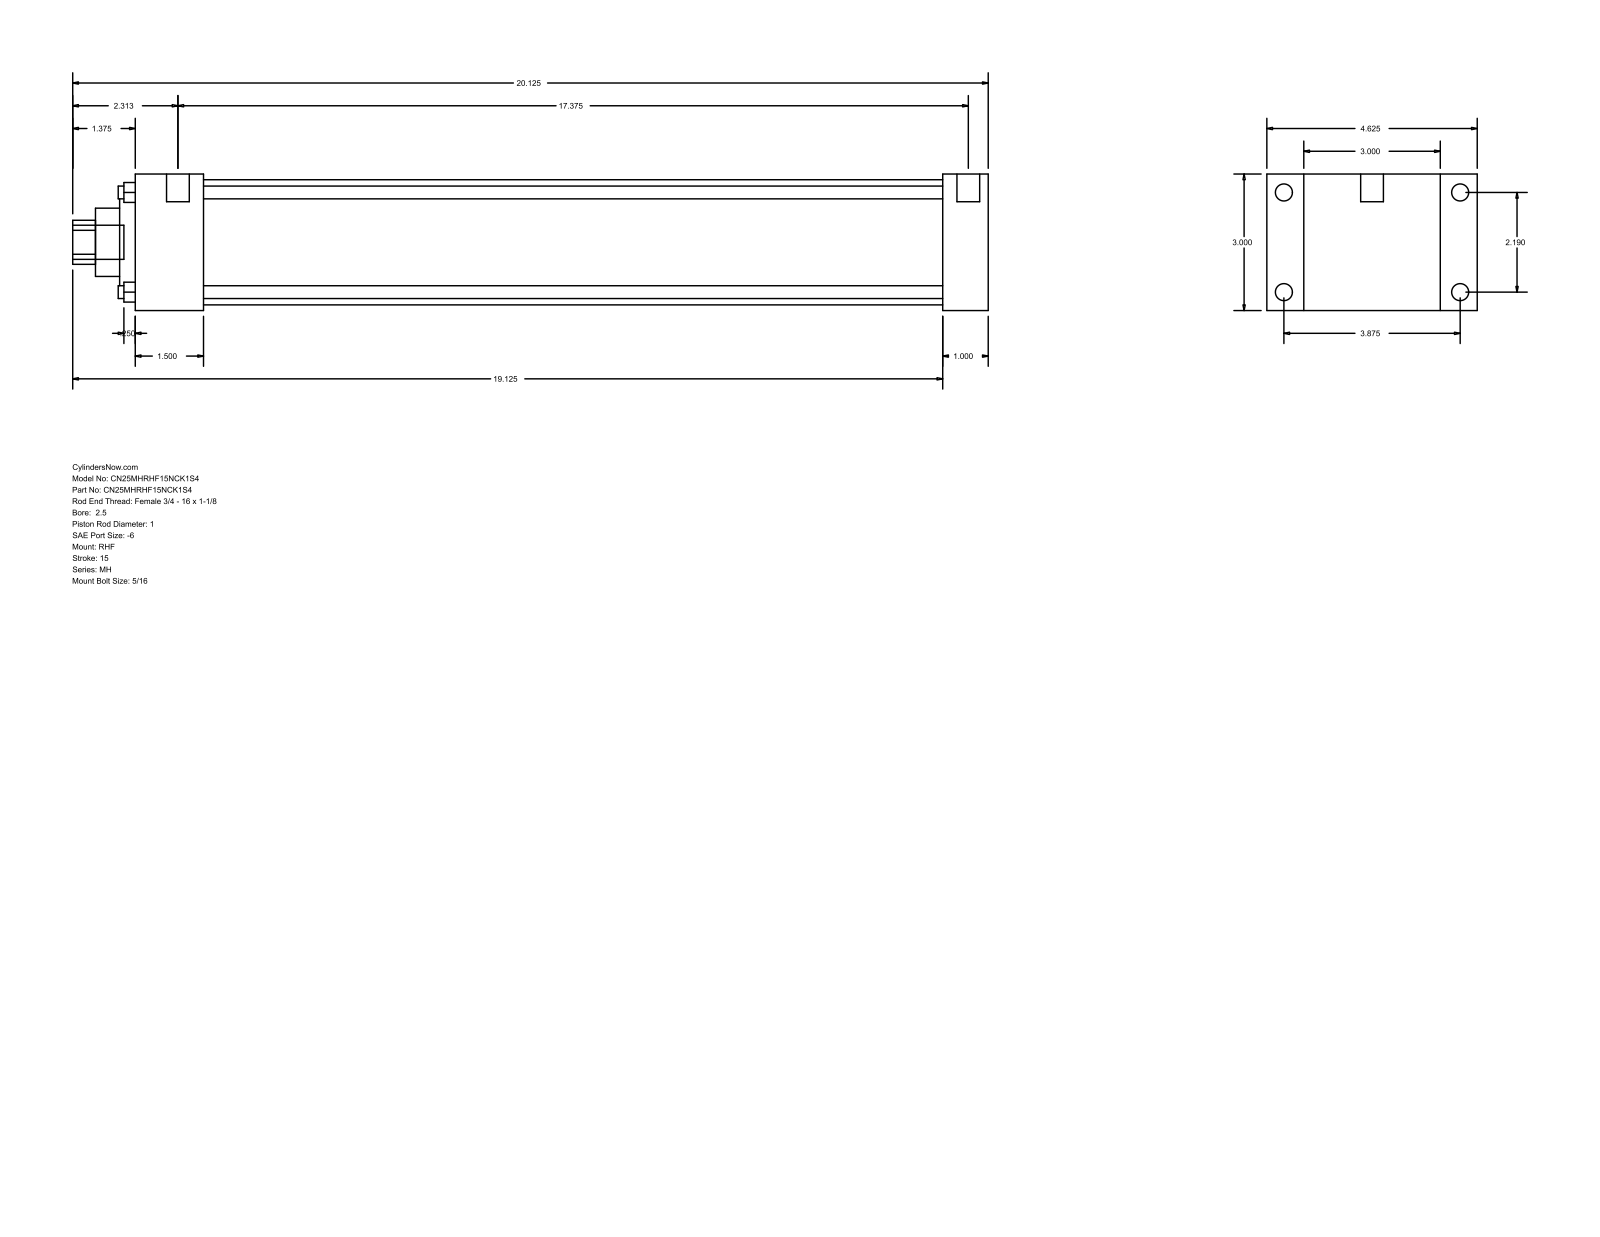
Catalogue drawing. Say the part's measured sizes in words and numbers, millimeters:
The part is named "MH_RHF__0250_1". Its 3-D file was written by "GSSL Pune (CONFIG_CONTROL_DESIGN)". It is 0 solids with 90 faces: 61 planar, 29 cylindrical and 0 other. Overall it measures 511.18 by 117.47 by 76.2 millimeters. Round holes: 4 of diameter 7.14, 1 of diameter 25.4, 1 of diameter 38.1, 1 of diameter 60.33, 1 of diameter 69.85. Round bosses or shafts: 4 of diameter 9.53, 4 of diameter 5.56, 2 of diameter 12.7, 1 of diameter 19.05. Partial cylindrical surfaces (rounded edges, fillets, slot ends): 1 of radius 12.29. The main face-to-face distances are 76.2, 25.41, 20.64, 96.84, 450.85, 476.26, 117.48, 38.11, 412.74, 438.15. The hole center spacings are 39.33, 55.62, 78.66.
